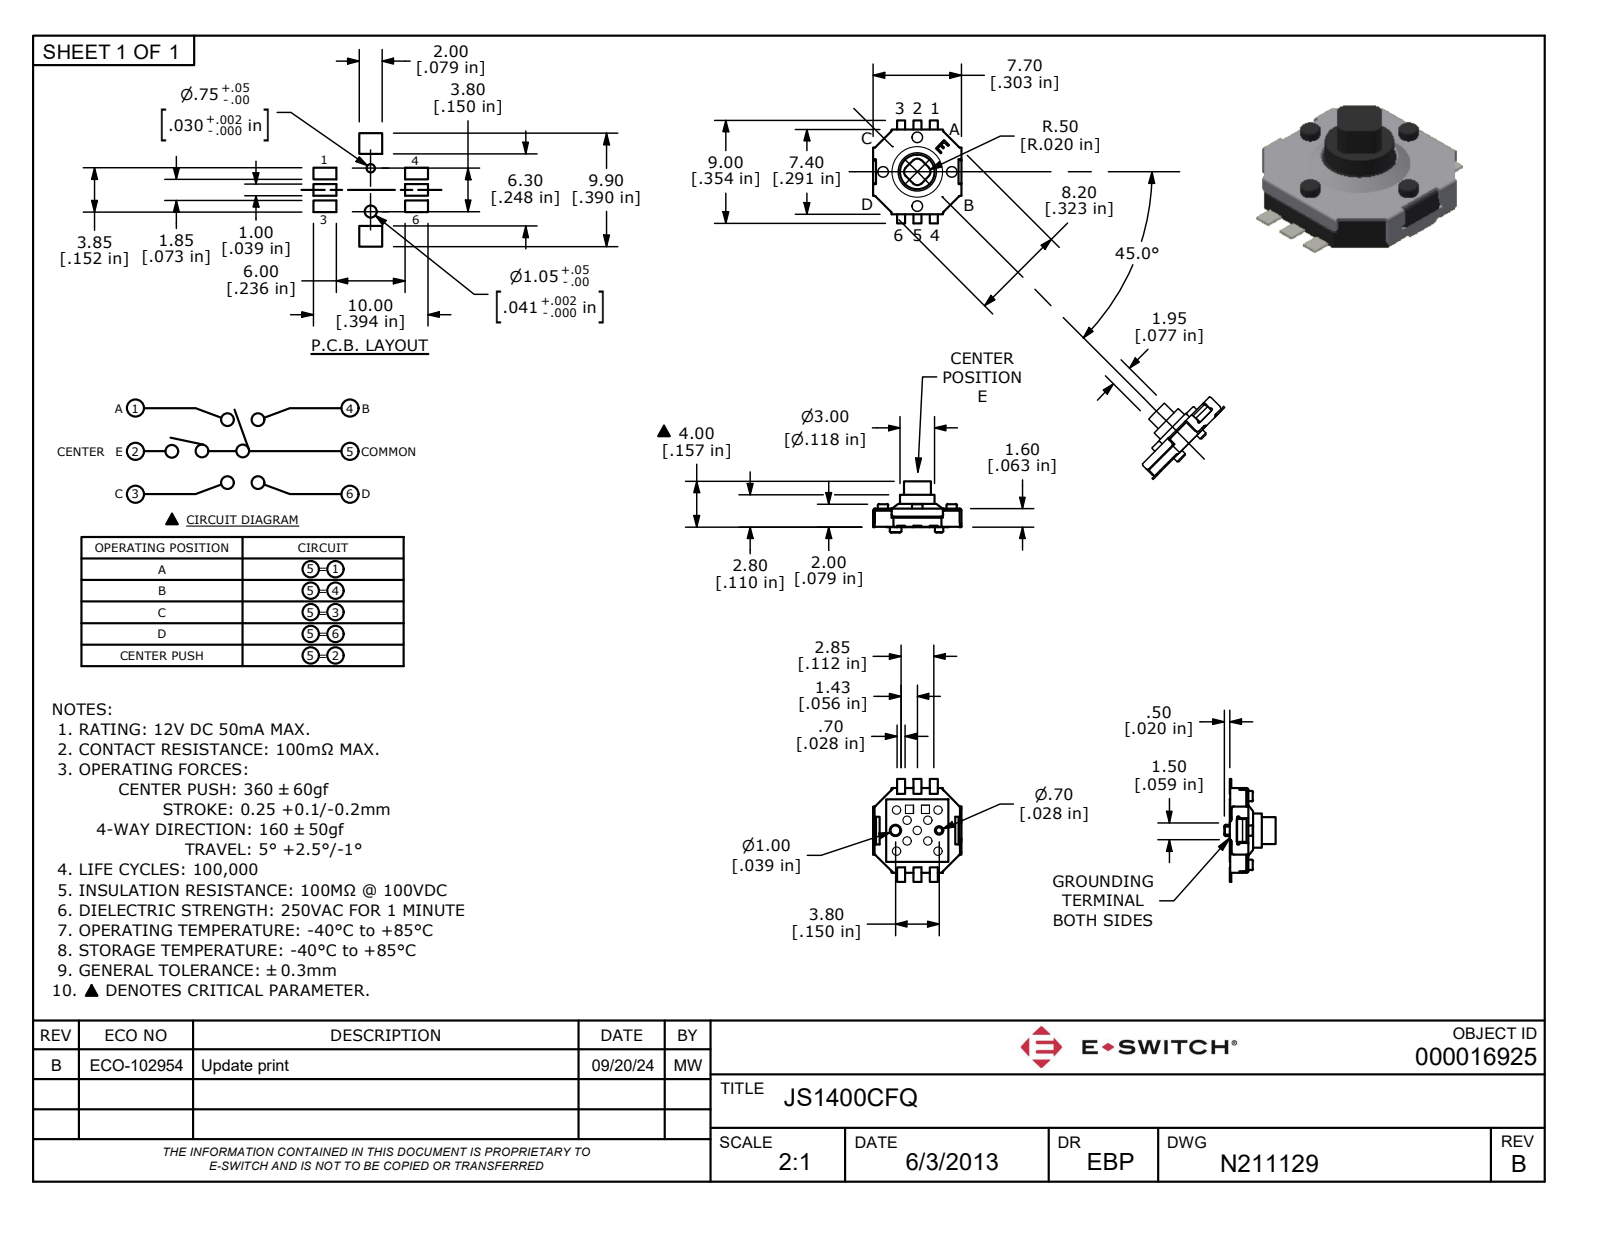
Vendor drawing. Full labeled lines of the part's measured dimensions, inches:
Part name (STEP PRODUCT): P:\\E-Switch Secure\\3D_MODELS_STP_FORMAT\\JS1400CFQ.stp
STEP written by: ACIS (CONFIG_CONTROL_DESIGN)
Units: inches
Bodies: 2 solids, 247 faces (193 planar, 44 cylindrical, 10 other)
Overall size (bounding box): 0.354 × 0.307 × 0.177
Volume: 0.005 in³ · Surface area: 0.502 in²
Round holes (diameter × count): ⌀0.028 ×9, ⌀0.03 ×4
Round bosses / shafts (diameter × count): ⌀0.028 ×5, ⌀0.035 ×4, ⌀0.118 ×1, ⌀0.039 ×1
Partial cylindrical surfaces — rounded edges, fillets, slot ends (radius × count): R0.02 ×4, R0.049 ×4
Main face-to-face distances: 0.022, 0.014, 0.035, 0.028, 0.041, 0.063, 0.057, 0.063, 0.057, 0.021
Hole centre spacings: 0.05, 0.085, 0.09, 0.112, 0.157, 0.202, 0.1, 0.071
